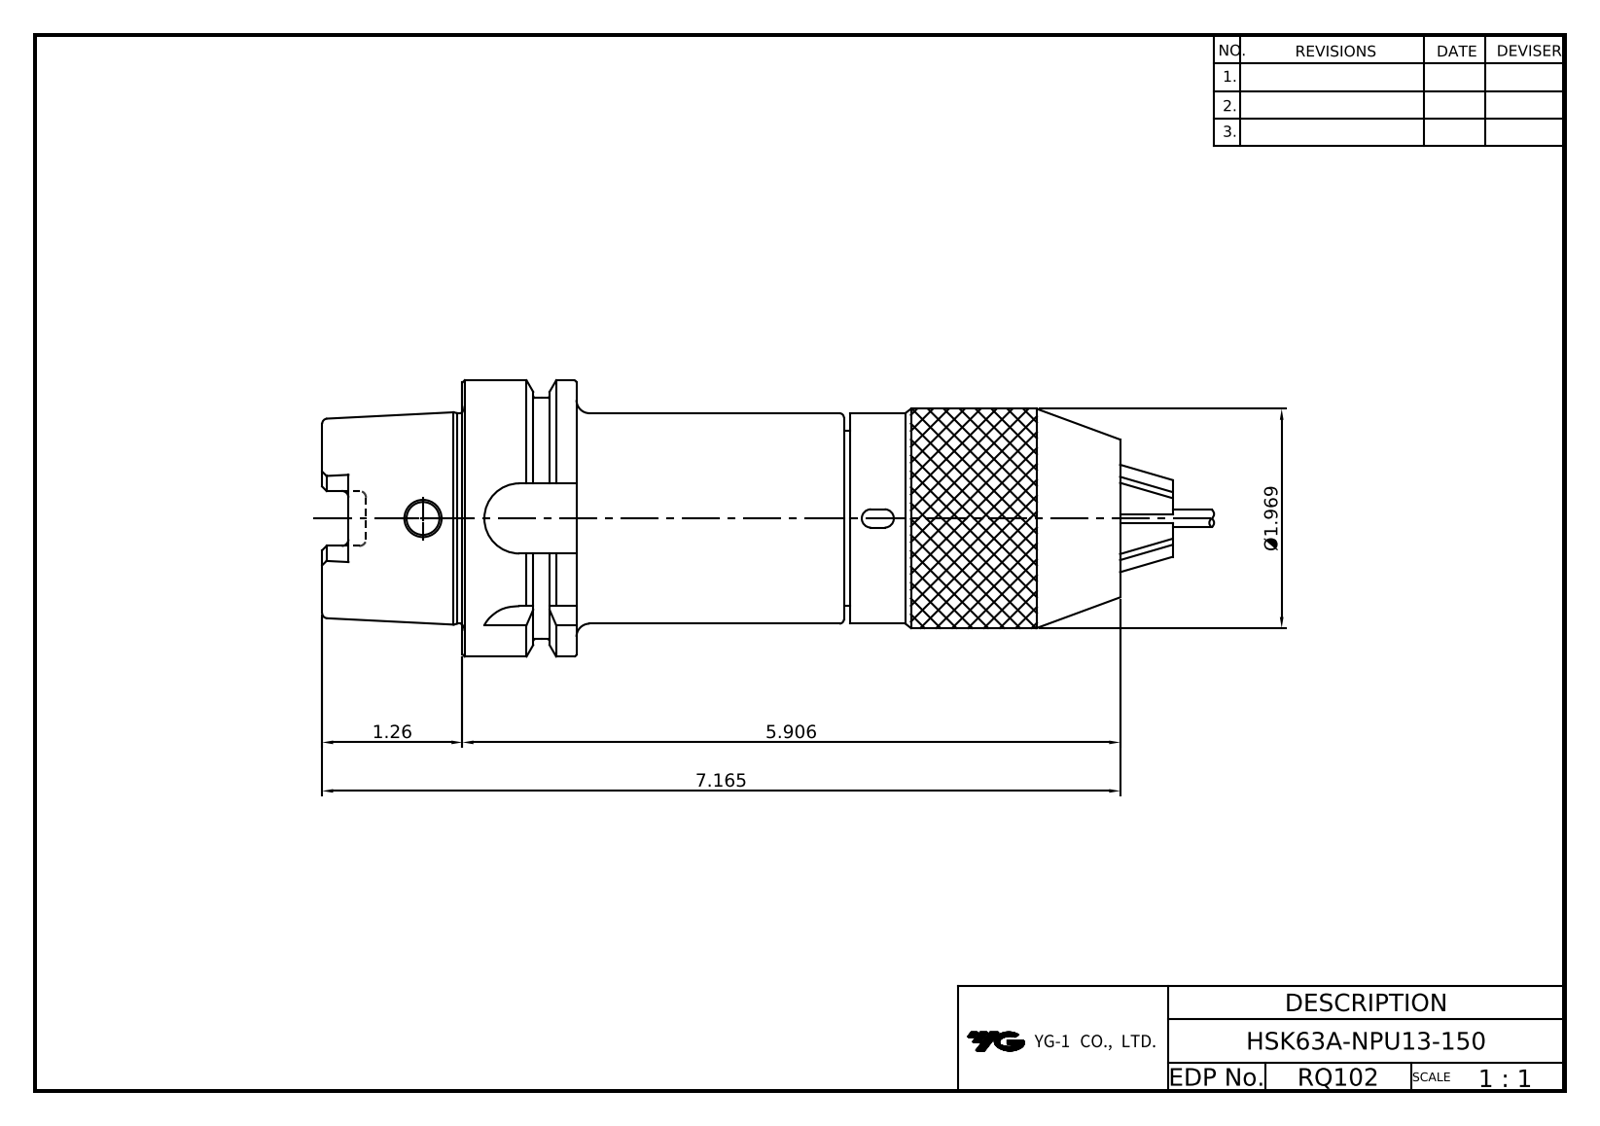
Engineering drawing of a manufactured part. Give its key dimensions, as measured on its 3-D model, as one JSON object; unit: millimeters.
{"part_name": "HSK63A-NPU13-150; NPU13; BB1271306M401A; BB12713070101A (+2 more)", "step_written_by": "Autodesk Inventor 2020 (AUTOMOTIVE_DESIGN)", "units": "millimeters", "bodies": {"solids": 7, "faces": 275, "planar": 158, "cylindrical": 59, "other": 58}, "overall_size": [193.53, 63, 63], "volume_mm3": 302555, "surface_area_mm2": 59810, "round_holes": [[7.5, 1], [9, 1], [10, 1], [14, 1], [16.92, 1], [19, 1], [23.5, 1], [34, 1], [38.5, 1], [40, 1], [44, 1]], "round_bosses_or_shafts": [[63, 1], [55, 1], [50, 1], [49.4, 1], [48.04, 1], [48, 1], [42, 1], [38, 1]], "partial_cylinders_radius": [[0.3, 6], [1.5, 6], [2.5, 6], [2.88, 4], [8, 4], [1, 3], [9, 3]], "face_to_face_distances": [31.5, 2.5, 80.5, 49, 101, 69.5, 150, 74.5, 16.5, 58.5]}
